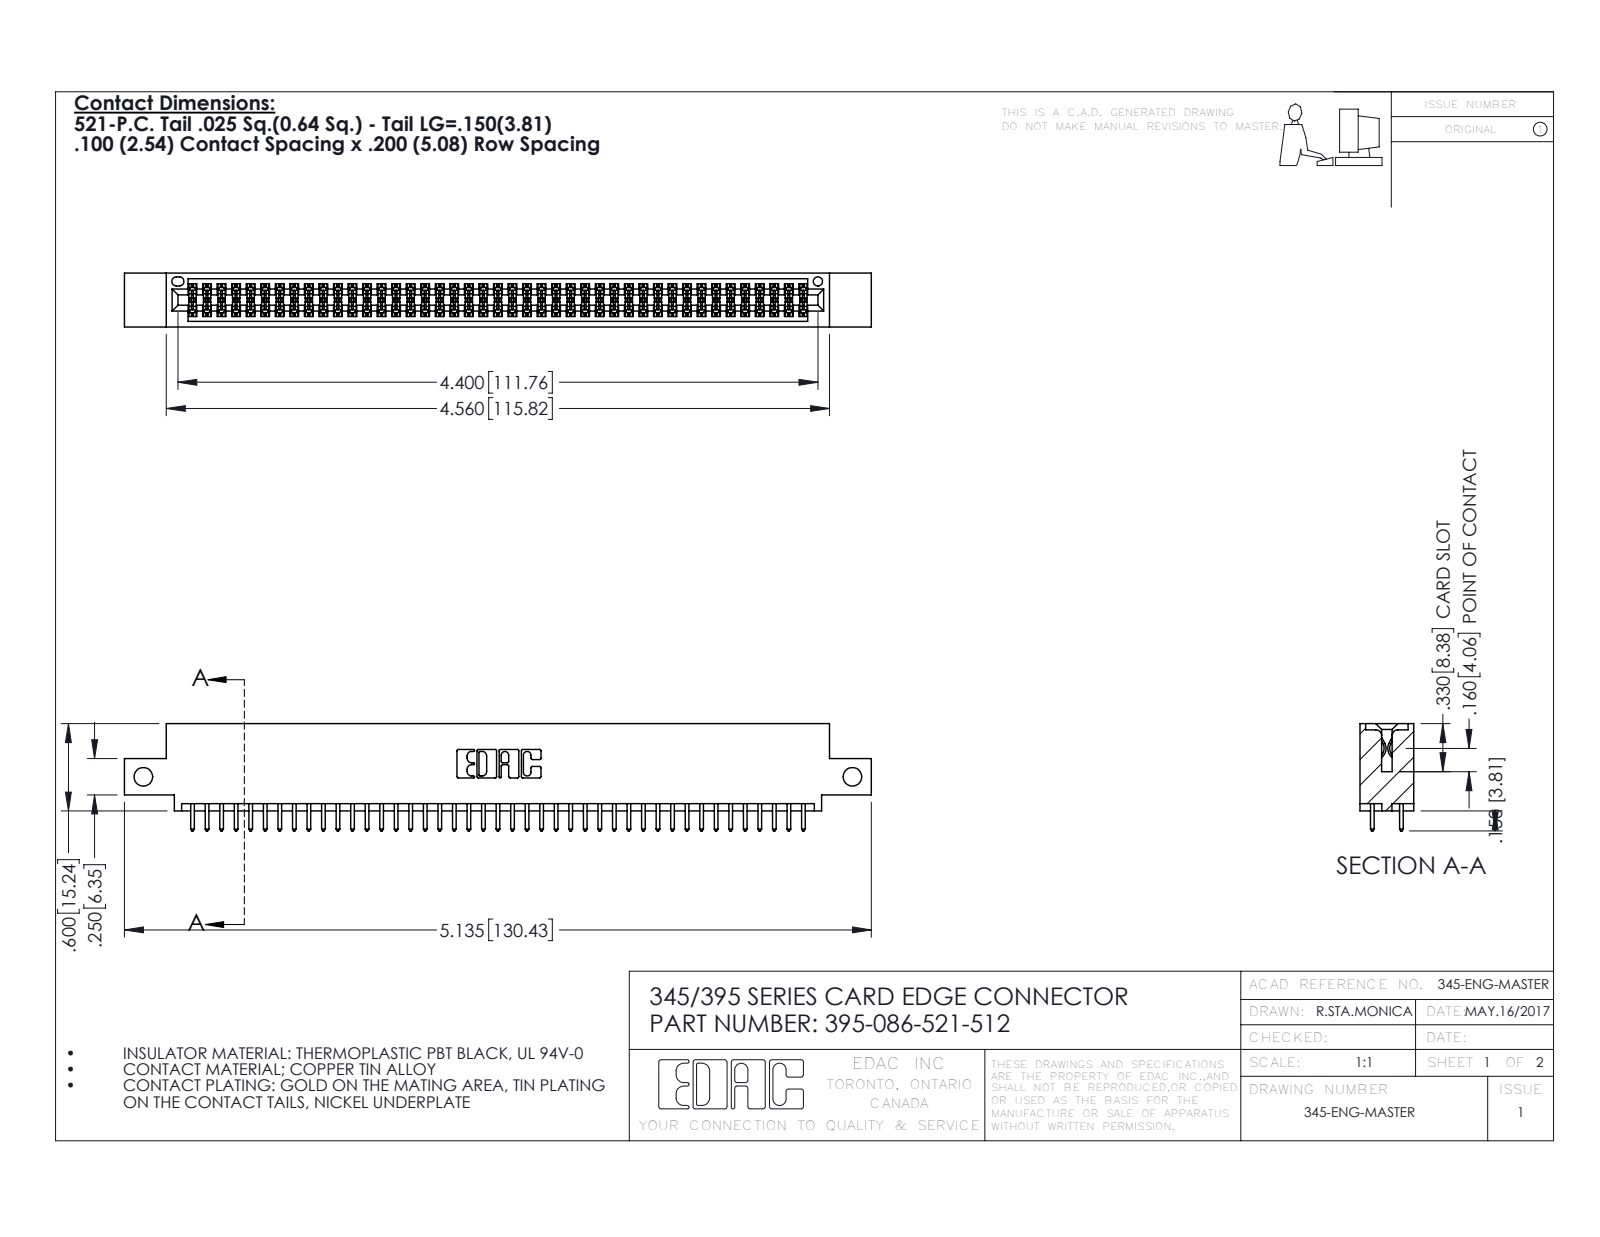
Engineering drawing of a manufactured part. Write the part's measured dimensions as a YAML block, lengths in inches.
part_name: "345-292-001_345-293-121; 345 Part_0.110 Offset - Side Mount; 395-086-521-512"
step_written_by: "SolidWorks 2016 (CONFIG_CONTROL_DESIGN)"
units: inches
bodies: {solids: 87, faces: 4430, planar: 2922, cylindrical: 1508, other: 0}
overall_size: [5.135, 0.737, 0.37]
volume: 0.762
surface_area: 28.21
round_holes:
  - {diameter: 0.128, count: 2}
  - {diameter: 0.064, count: 1}
partial_cylinders:
  - {radius: 0.006, count: 129}
  - {radius: 0.01, count: 86}
  - {radius: 0.01, count: 22}
  - {radius: 0.007, count: 6}
  - {radius: 0.031, count: 6}
  - {radius: 0.026, count: 3}
  - {radius: 0.014, count: 2}
  - {radius: 0.019, count: 2}
face_to_face_distances: [0.298, 0.072, 0.2, 0.37, 0.098, 0.272, 0.025, 0.225, 0.175, 0.149]
hole_center_spacings: [4.875]
